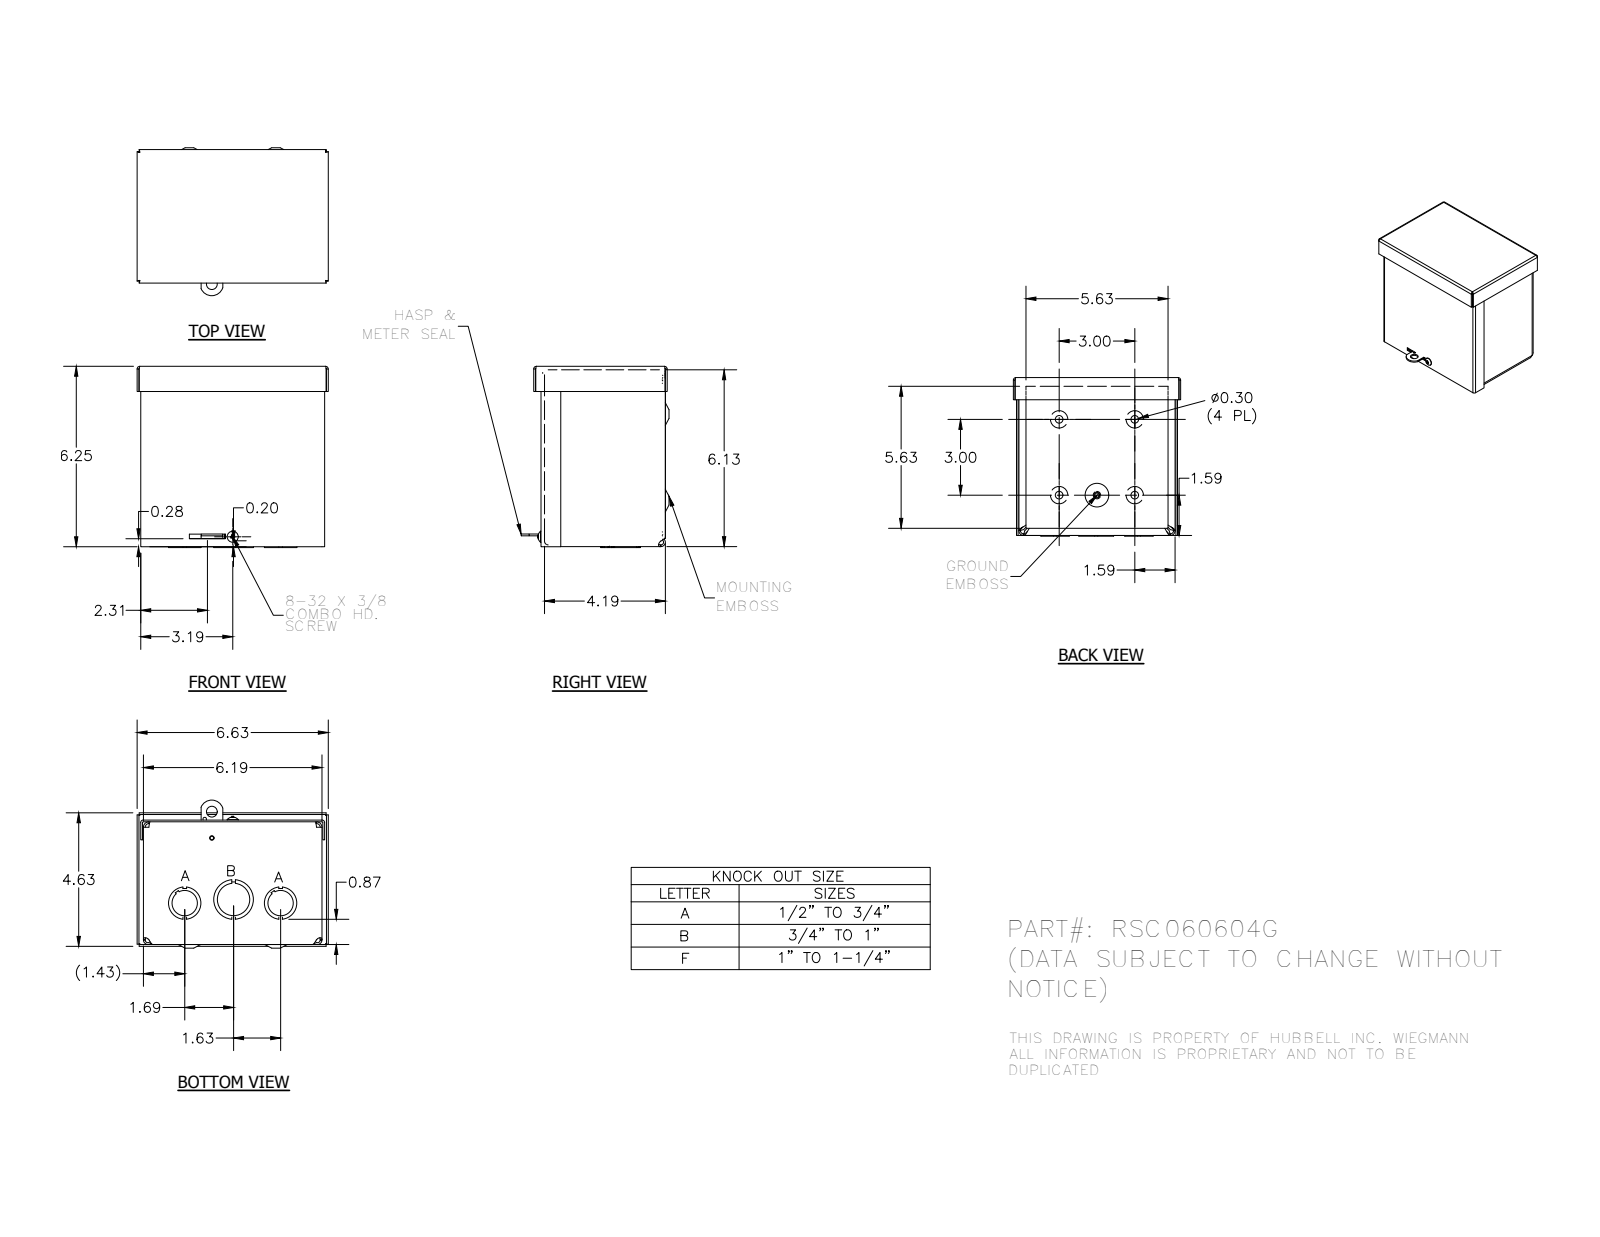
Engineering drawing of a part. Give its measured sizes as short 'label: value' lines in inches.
name: RSC060604G_WRAP; RSC0606G_LID; RSC0604G_CAP; 3183 (+4 more)
written by: Autodesk Inventor 2014 (AUTOMOTIVE_DESIGN)
unit: in
bodies: 6 solids, 461 faces (220 planar, 116 cylindrical, 125 other)
size: 6.625 × 6.281 × 5.125
volume: 16.05 in³; area: 529.5 in²
holes: 4× ⌀0.3, 3× ⌀1.125, 2× ⌀0.125, 2× ⌀0.313, 2× ⌀0.875, 1× ⌀0.148, 1× ⌀0.156, 1× ⌀0.165, 1× ⌀0.375, 1× ⌀1.375
bosses: 1× ⌀0.384, 1× ⌀0.228, 1× ⌀0.164
rounds: 10× R0.01, 8× R0.031, 8× R0.093, 8× R0.125, 8× R0.187, 4× R0.021, 4× R0.031, 4× R0.055
face distances: 0.062, 6.126, 0.062, 4.249, 6.188, 0.124, 4.187, 0.063, 4.312, 4.25
hole spacings: 3, 1.5, 3.354, 4.243, 0.358, 0.702, 0.913, 1.252
